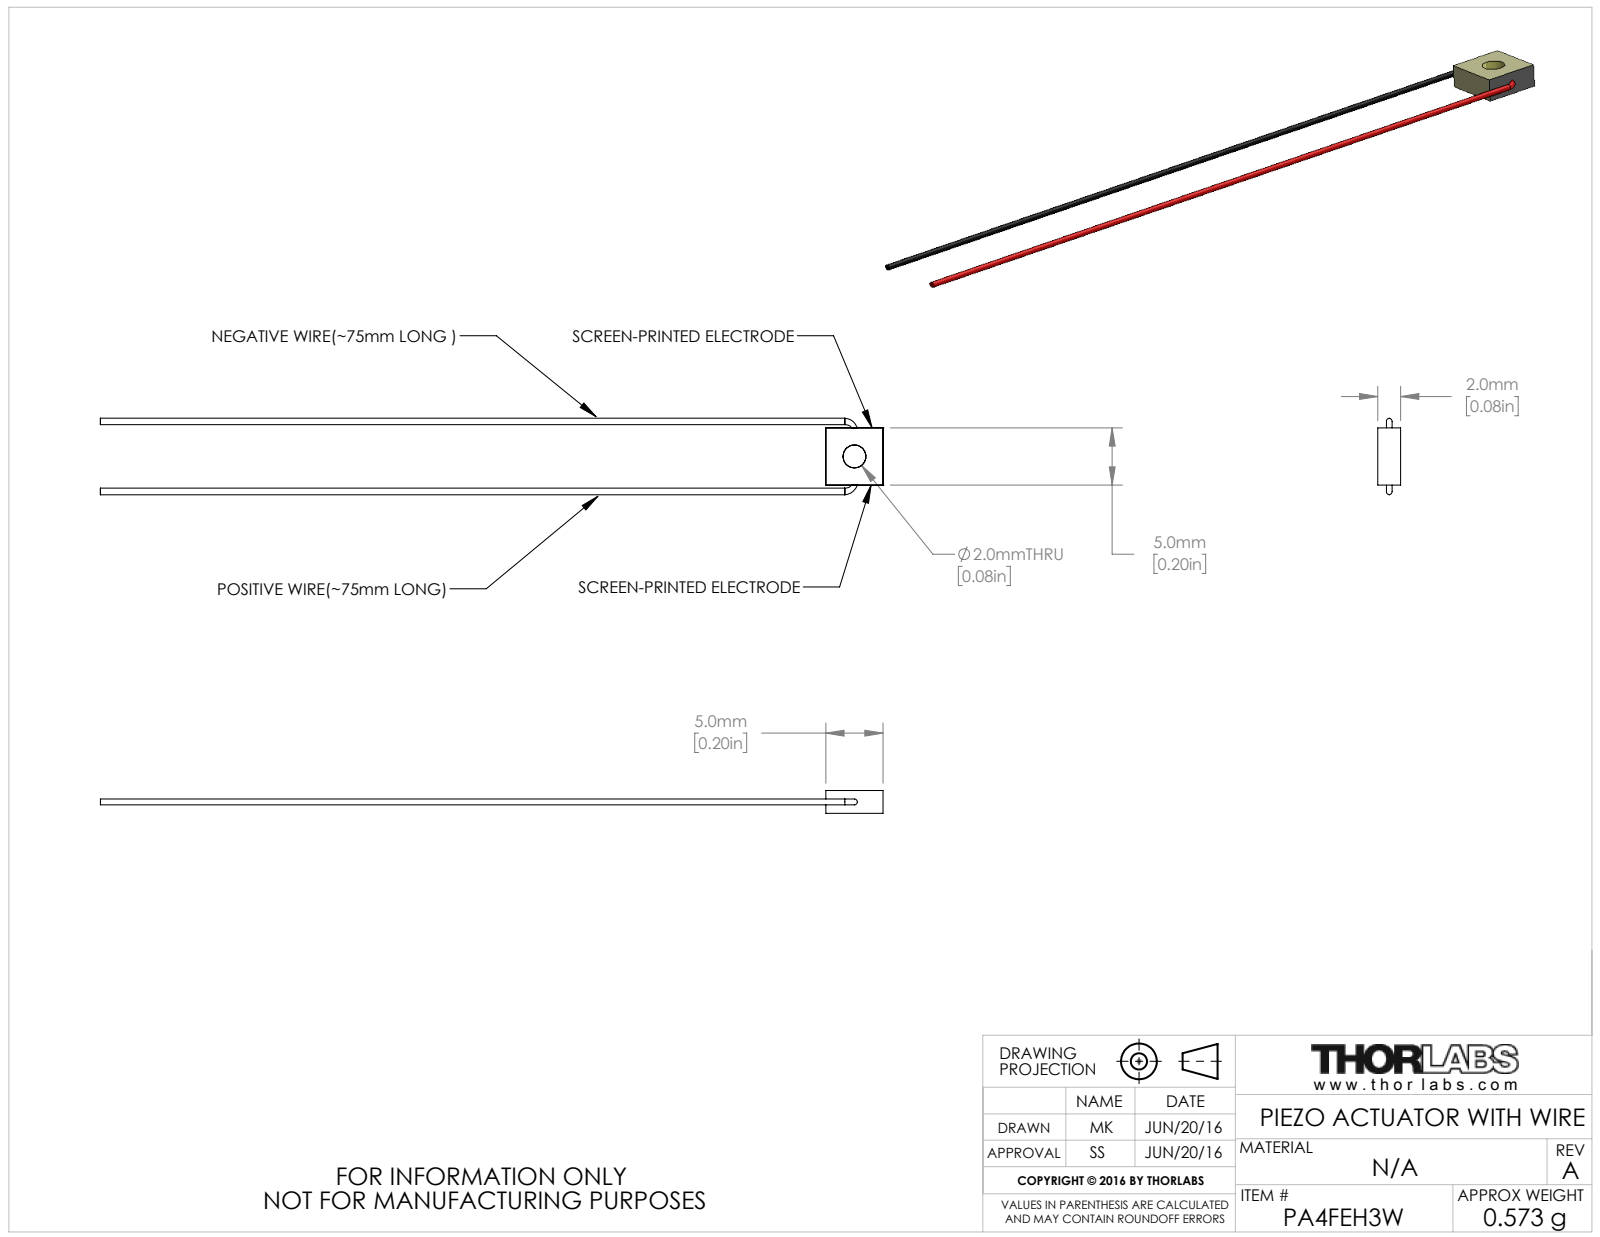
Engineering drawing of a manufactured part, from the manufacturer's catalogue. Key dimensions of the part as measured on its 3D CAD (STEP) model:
Part name (STEP PRODUCT): CTN008936
STEP written by: SolidWorks 2016 (AUTOMOTIVE_DESIGN)
Units: millimetres
Bodies: 1 solid, 18 faces (8 planar, 2 cylindrical, 8 other)
Overall size (bounding box): 68.34 × 6.67 × 2
Volume: 73 mm³ · Surface area: 318 mm²
Round holes (diameter × count): ⌀2 ×1
Main face-to-face distances: 2, 5, 68.34, 63.34
